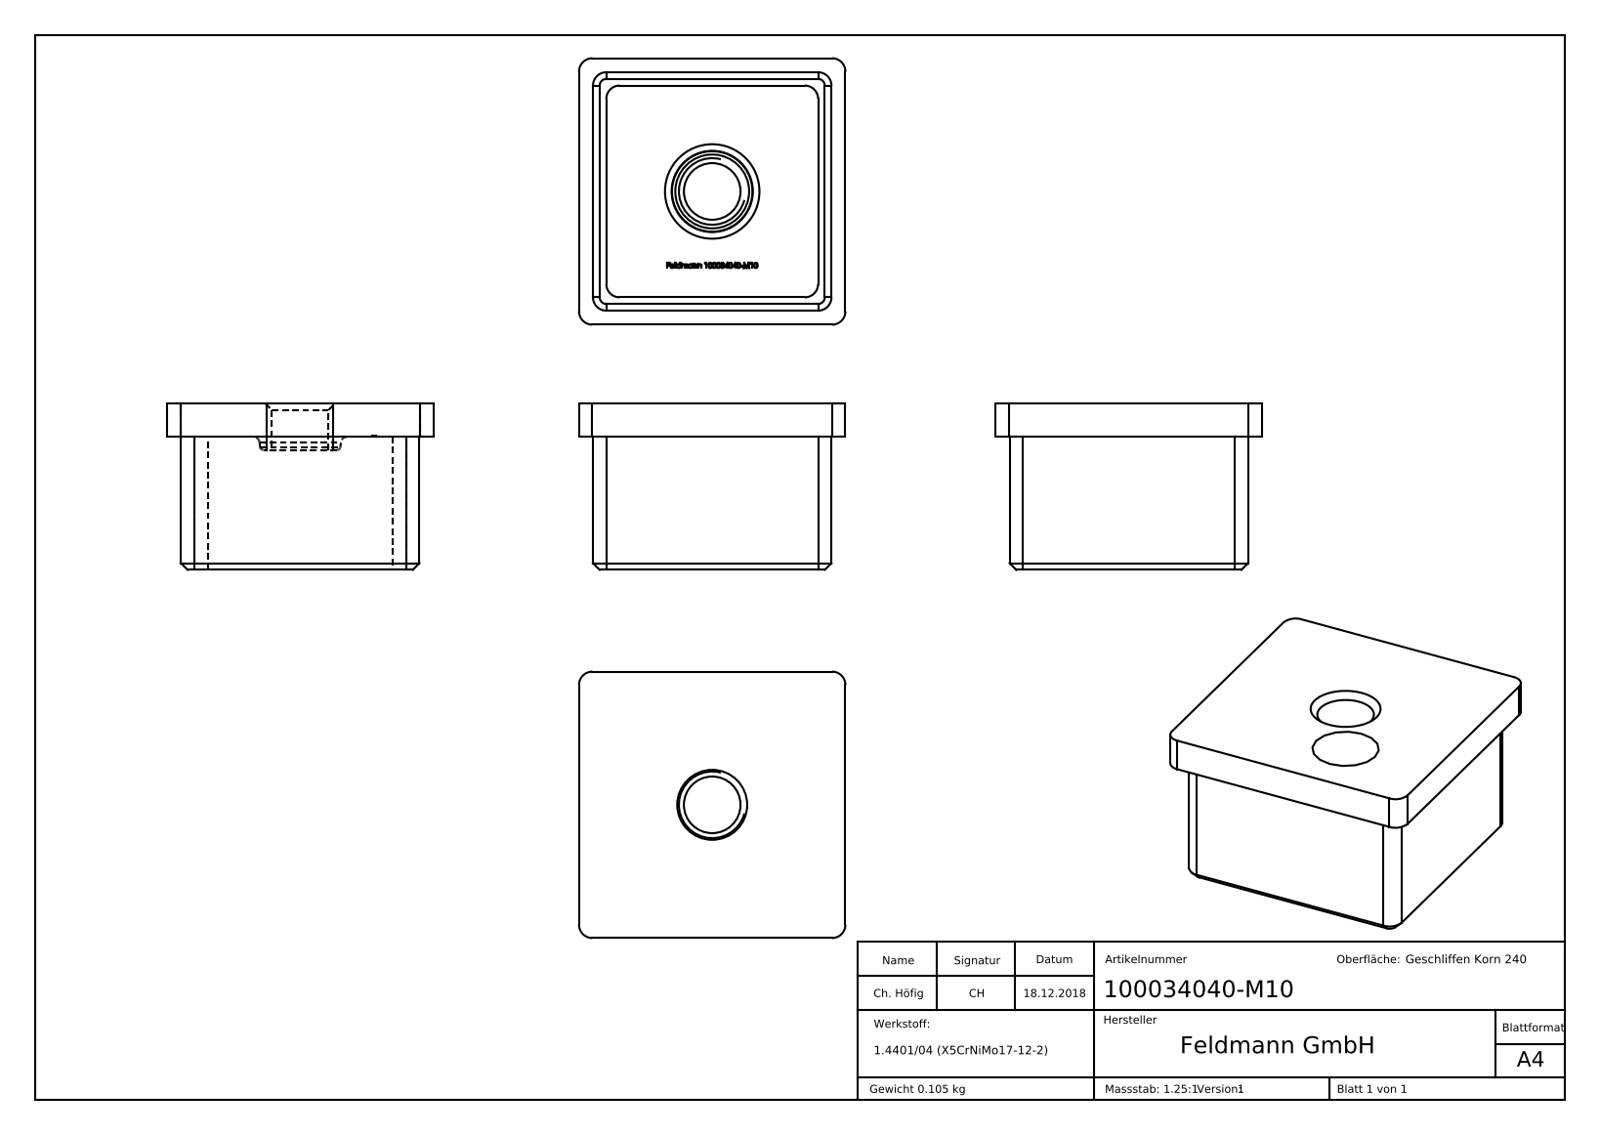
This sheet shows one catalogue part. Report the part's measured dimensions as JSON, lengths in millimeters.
{"part_name": "100034040-M10", "step_written_by": "SolidWorks 2015 (CONFIG_CONTROL_DESIGN)", "units": "millimeters", "bodies": {"solids": 1, "faces": 307, "planar": 165, "cylindrical": 14, "other": 128}, "overall_size": [40, 40, 25], "volume_mm3": 13148, "surface_area_mm2": 9280, "round_holes": [[8.5, 1]], "partial_cylinders_radius": [[2, 12]], "face_to_face_distances": [2, 33.8, 35.8, 5, 31.8, 2.1, 4.1, 35.9, 37.9, 40]}
